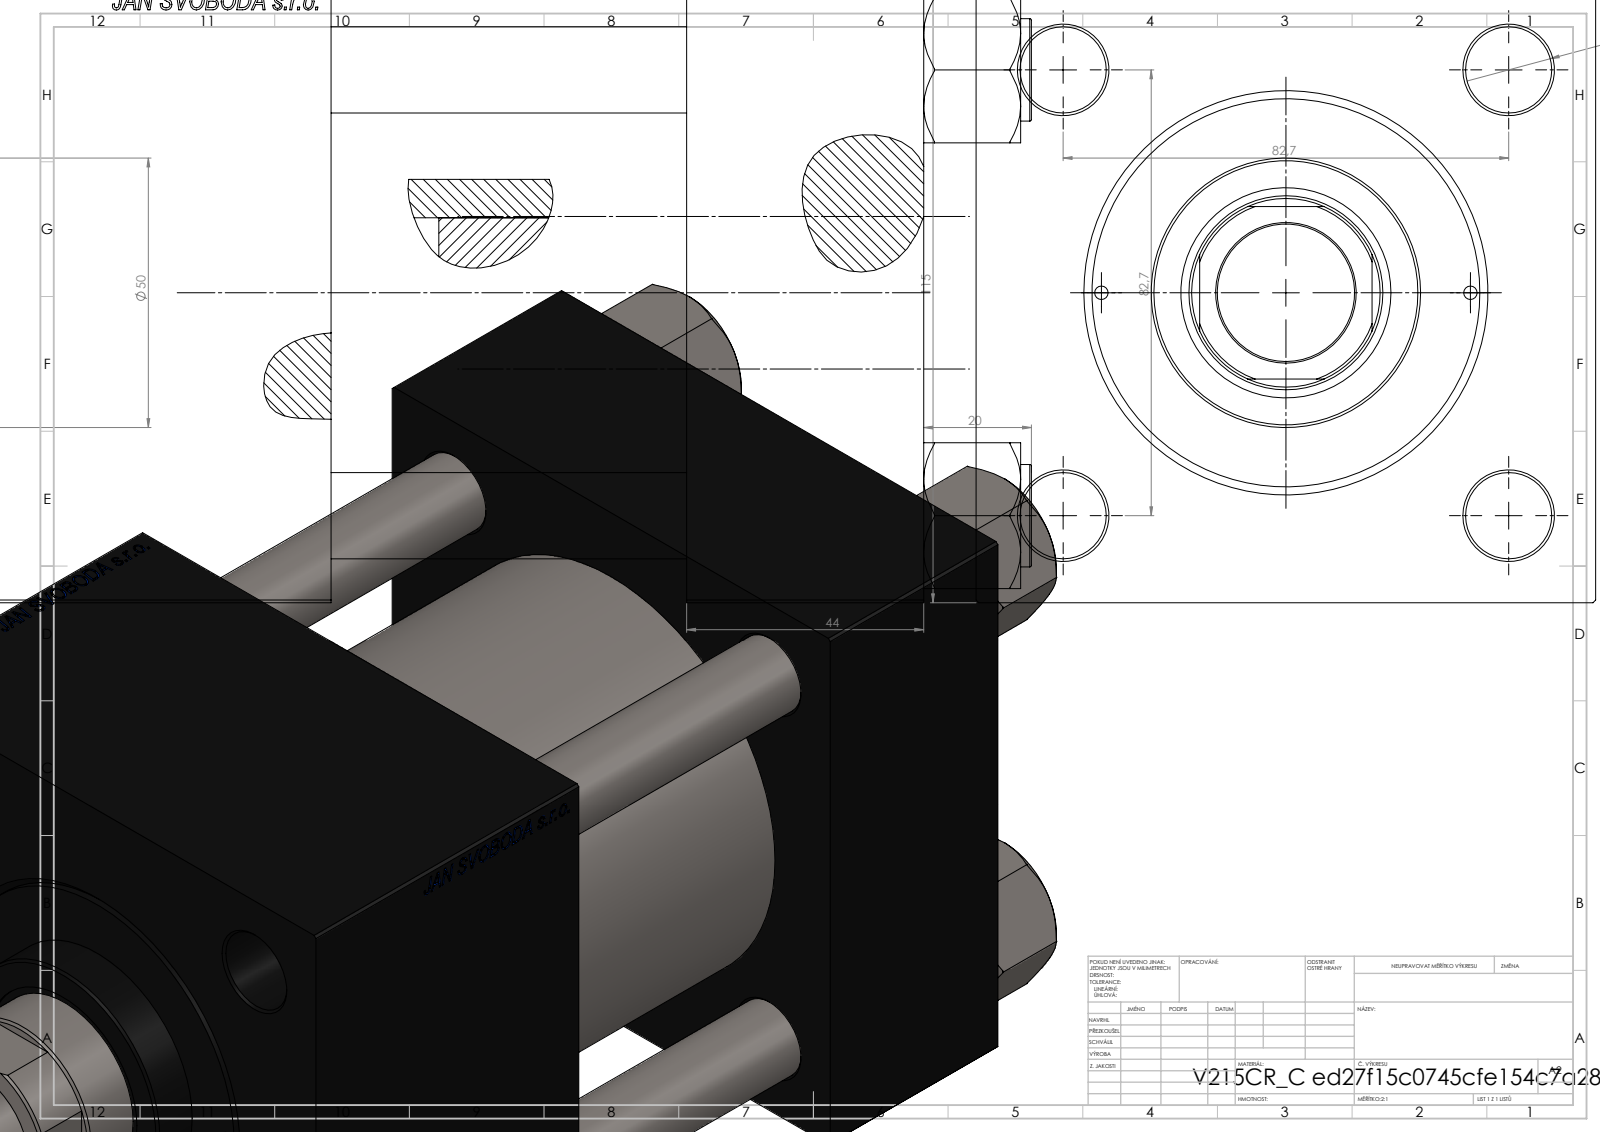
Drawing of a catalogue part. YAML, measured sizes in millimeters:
part_name: "V215CR_VCP_C; V215_VC_A; NUT_M5_C; V215CR_C_TYCINKA (+1 more)"
step_written_by: "SolidWorks 2019 (CONFIG_CONTROL_DESIGN)"
units: millimeters
bodies: {solids: 11, faces: 1203, planar: 576, cylindrical: 91, other: 536}
overall_size: [230, 115, 115]
volume: 1786000
surface_area: 268514
round_holes:
  - {diameter: 16, count: 4}
  - {diameter: 2.5, count: 2}
  - {diameter: 7, count: 2}
  - {diameter: 26.44, count: 2}
  - {diameter: 35, count: 2}
  - {diameter: 25.5, count: 1}
  - {diameter: 36, count: 1}
  - {diameter: 39, count: 1}
  - {diameter: 61, count: 1}
  - {diameter: 72, count: 1}
  - {diameter: 80, count: 1}
round_bosses_or_shafts:
  - {diameter: 19, count: 4}
  - {diameter: 86, count: 1}
  - {diameter: 50, count: 1}
partial_cylinders:
  - {radius: 17.5, count: 1}
face_to_face_distances: [115, 44, 179, 135, 110, 69, 66, 20, 150.3, 106.3]
hole_center_spacings: [41.96, 58.48, 82.7, 86.17, 34.25, 116.96, 68.5, 111]
